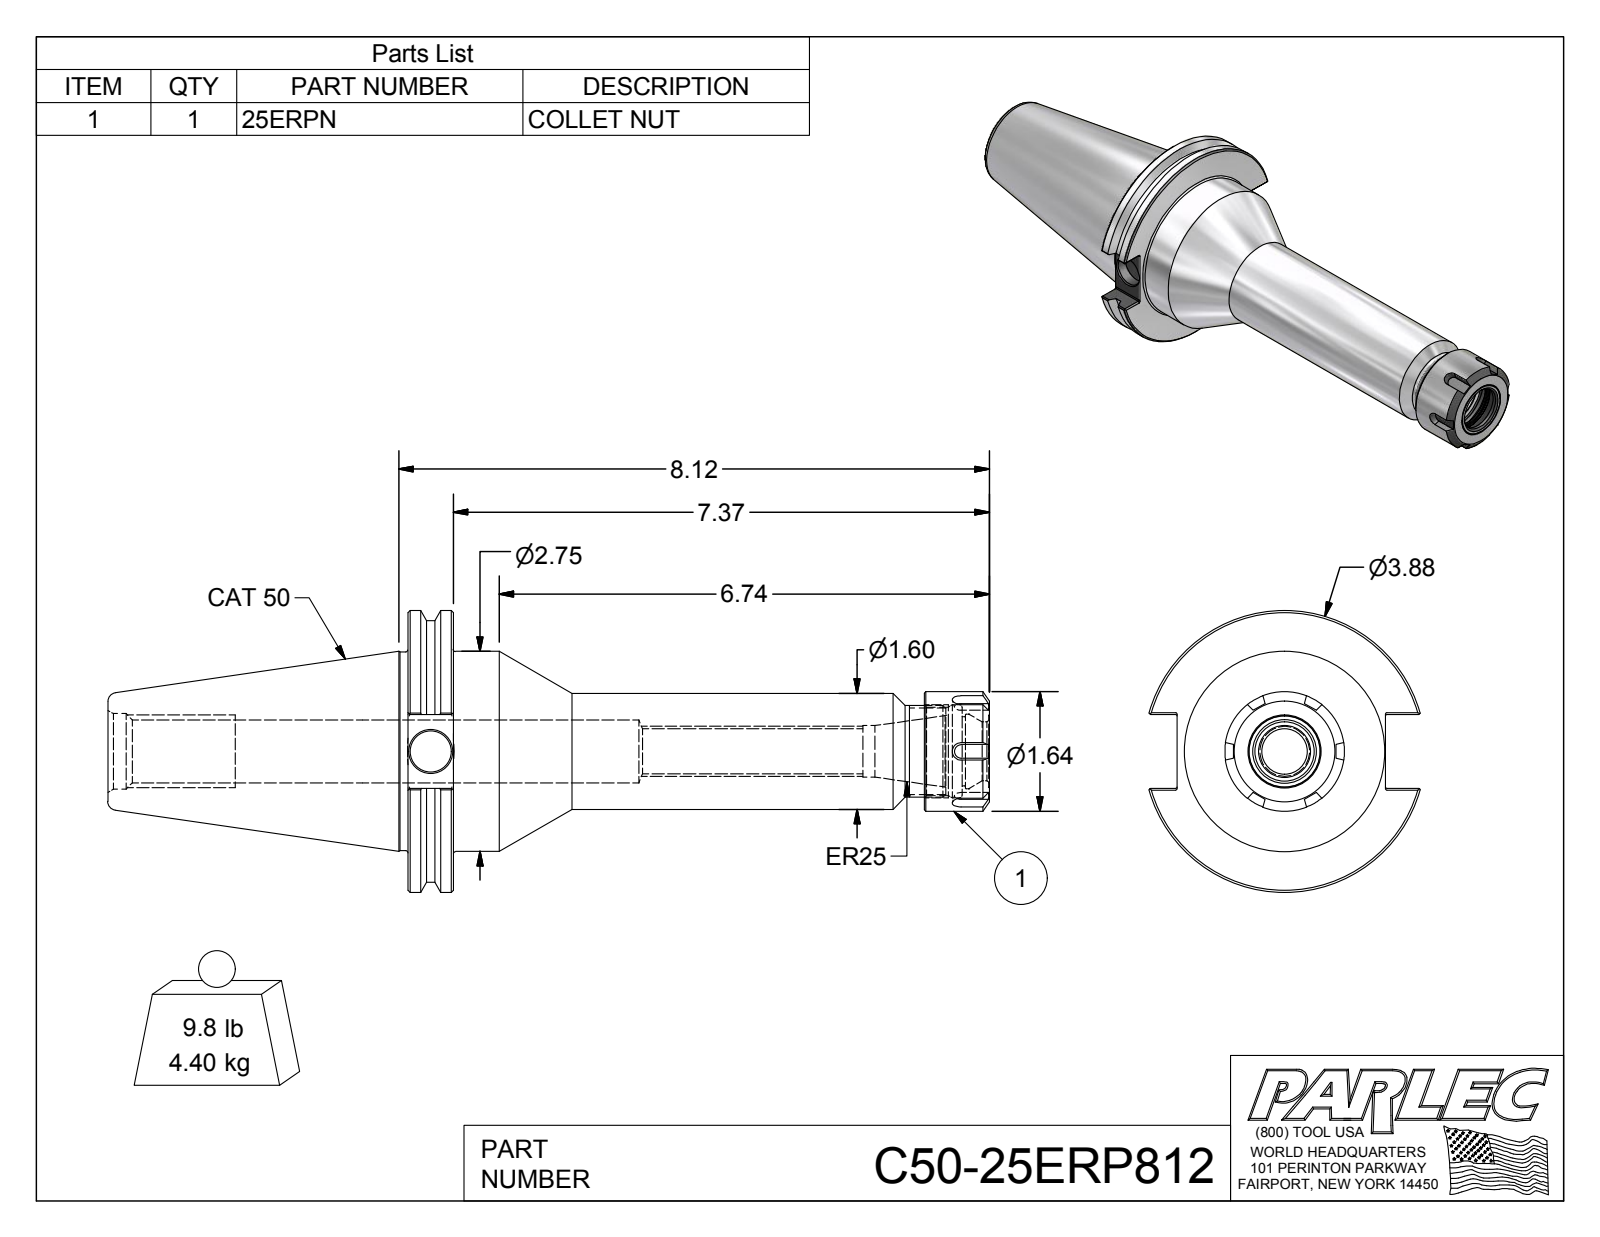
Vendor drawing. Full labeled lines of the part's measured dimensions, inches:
Part name (STEP PRODUCT): C50-25ERP812; C50-25ER8-1; 25ERPN
STEP written by: Autodesk Inventor 2012 (AUTOMOTIVE_DESIGN)
Units: inches
Bodies: 2 solids, 125 faces (51 planar, 31 cylindrical, 43 other)
Overall size (bounding box): 12.12 × 3.875 × 3.729
Volume: 34.58 in³ · Surface area: 128.8 in²
Round holes (diameter × count): ⌀0.315 ×1, ⌀0.399 ×1, ⌀0.62 ×1, ⌀0.71 ×1, ⌀0.811 ×1, ⌀0.864 ×1, ⌀0.865 ×1, ⌀0.95 ×1, ⌀1.027 ×1, ⌀1.038 ×1, ⌀1.217 ×1, ⌀1.28 ×1
Round bosses / shafts (diameter × count): ⌀3.875 ×1, ⌀3.594 ×1, ⌀2.75 ×1, ⌀2.73 ×1, ⌀1.643 ×1, ⌀1.595 ×1, ⌀1.26 ×1
Partial cylindrical surfaces — rounded edges, fillets, slot ends (radius × count): R0.02 ×8
Main face-to-face distances: 0.625, 7.995, 7.37, 7.102, 6.477, 0.893, 4.125, 4.75, 11.227, 12.12
